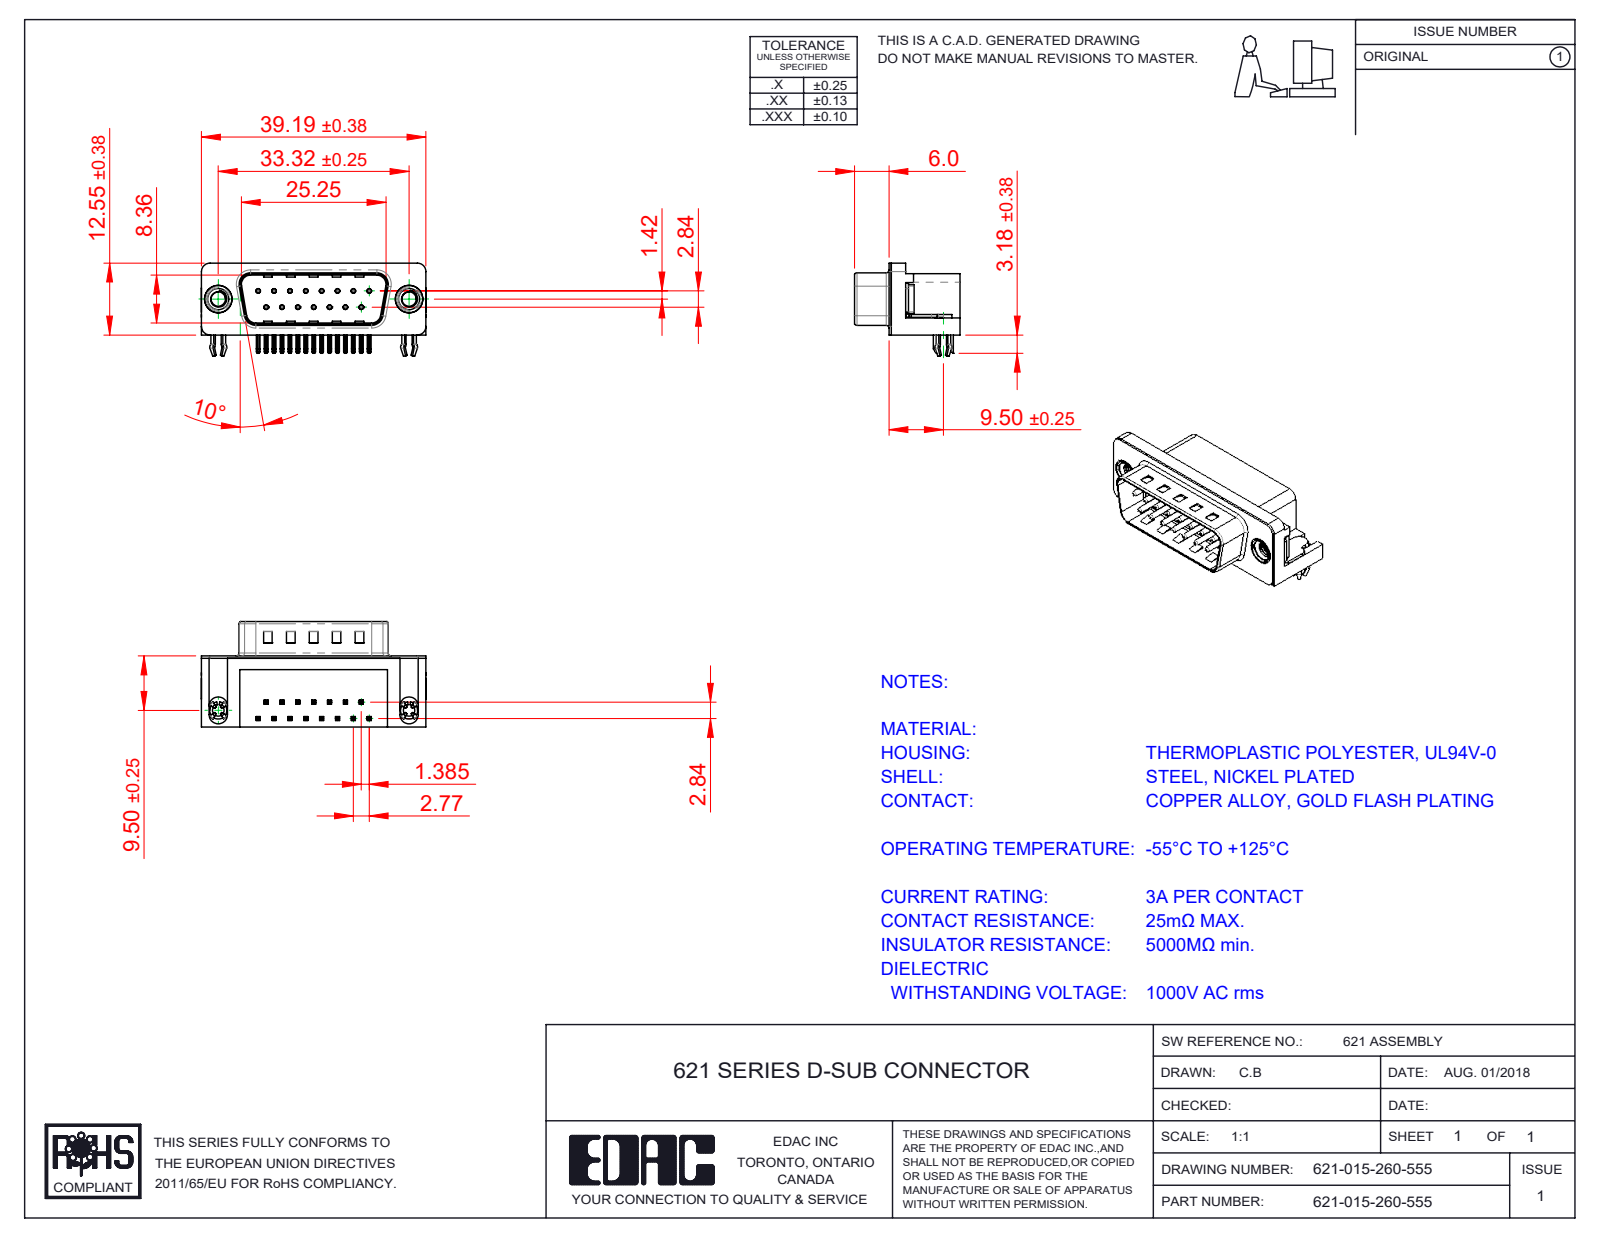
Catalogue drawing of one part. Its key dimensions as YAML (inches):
part_name: "621 Contact Top; 621 Contact Bottom; 621-015-260-555; 621 M3 Threaded Rivet (+3 more)"
step_written_by: "SolidWorks 2016 (CONFIG_CONTROL_DESIGN)"
units: inches
bodies: {solids: 21, faces: 1507, planar: 893, cylindrical: 461, other: 153}
overall_size: [1.544, 0.724, 0.619]
volume: 0.27
surface_area: 8.886
round_holes:
  - {diameter: 0.014, count: 15}
  - {diameter: 0.031, count: 15}
  - {diameter: 0.089, count: 2}
  - {diameter: 0.098, count: 2}
  - {diameter: 0.157, count: 2}
  - {diameter: 0.189, count: 2}
  - {diameter: 0.197, count: 2}
round_bosses_or_shafts:
  - {diameter: 0.03, count: 15}
  - {diameter: 0.193, count: 2}
  - {diameter: 0.187, count: 2}
  - {diameter: 0.154, count: 2}
  - {diameter: 0.128, count: 2}
partial_cylinders:
  - {radius: 0.01, count: 68}
  - {radius: 0.005, count: 30}
  - {radius: 0.039, count: 16}
  - {radius: 0.02, count: 9}
  - {radius: 0.063, count: 8}
  - {radius: 0.059, count: 6}
  - {radius: 0.035, count: 4}
  - {radius: 0.079, count: 4}
face_to_face_distances: [0.016, 0.472, 0.407, 0.083, 0.412, 0.488, 0.067, 0.428, 0.345, 0.114]
hole_center_spacings: [0.124, 0.109, 0.218, 0.327, 0.436, 0.198, 0.198, 0.294]
